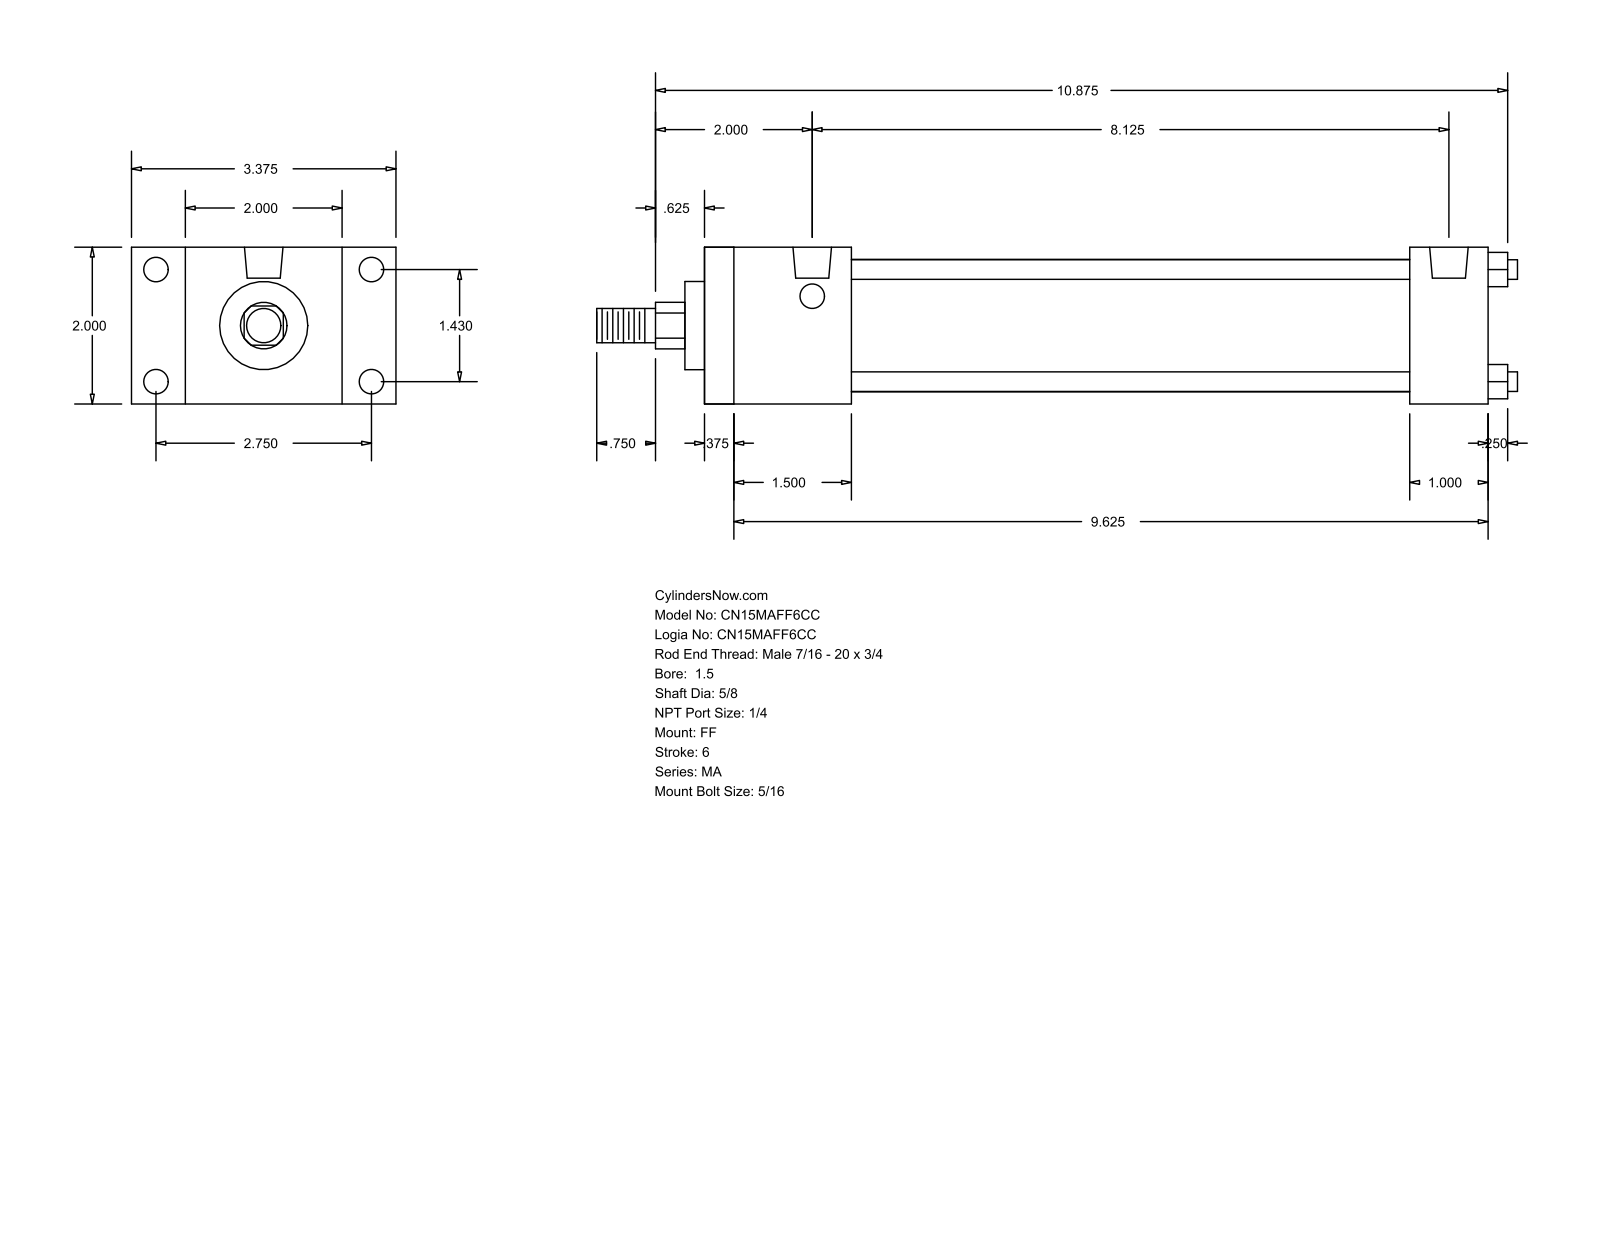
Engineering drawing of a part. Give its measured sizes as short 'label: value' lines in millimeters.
name: MA_FF__0150_0.625
written by: GSSL Pune (CONFIG_CONTROL_DESIGN)
unit: mm
bodies: 0 solids, 92 faces (64 planar, 28 cylindrical, 0 other)
size: 298.45 × 85.72 × 50.8
holes: 8× ⌀7.94, 2× ⌀12.49
bosses: 4× ⌀6.35, 1× ⌀42.93, 1× ⌀28.57, 1× ⌀15.88, 1× ⌀11.11
rounds: 1× R7.54
face distances: 50.8, 254, 9.52, 244.48, 47.62, 228.59, 38.1, 219.07, 180.97, 206.38
hole spacings: 36.32, 69.84, 78.72, 206.38
